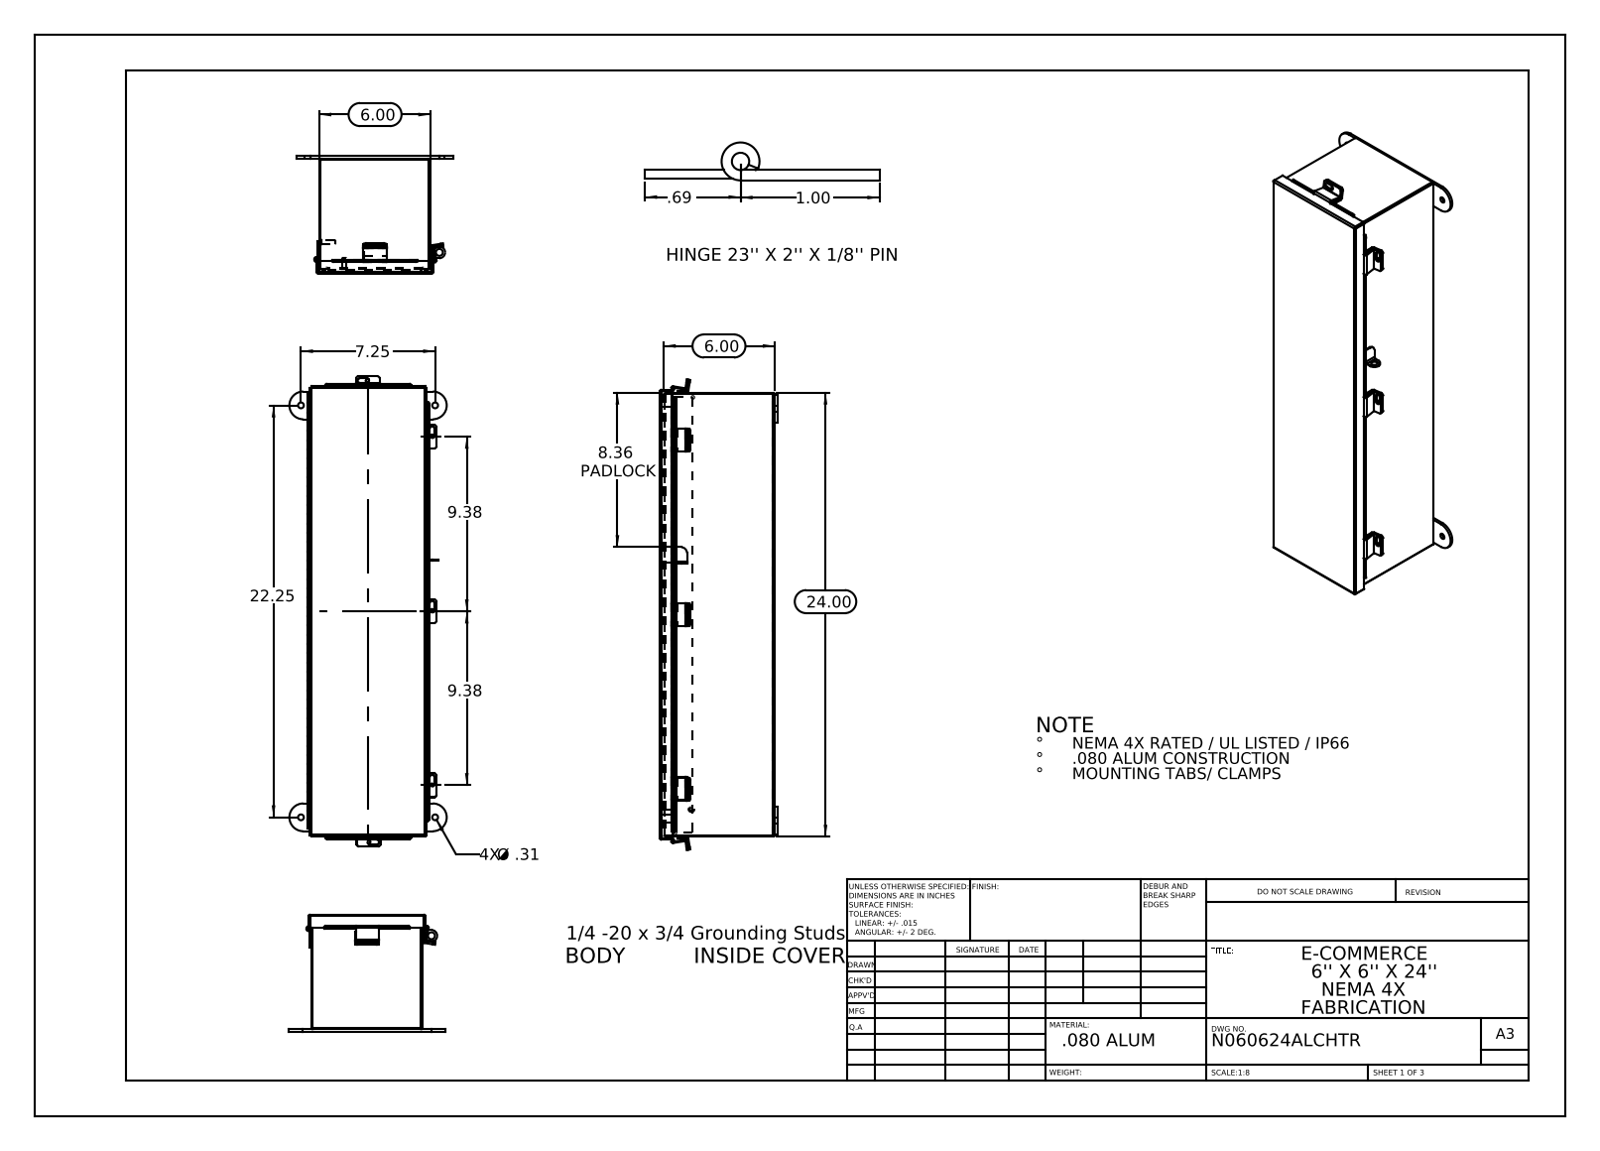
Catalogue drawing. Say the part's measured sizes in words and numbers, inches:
The part is named "N060624SSCHTR JIC Cover Clamp; N060624SSCHTR; N060624SSCHTR Mounting Bracket; N060624SSCHTR JIC Bottom (+8 more)". Its 3-D file was written by "SolidWorks 2013 (CONFIG_CONTROL_DESIGN)". It is 21 solids with 898 faces: 553 planar, 325 cylindrical and 20 other. Overall it measures 25.407 by 8.5 by 6.337 inches. Its volume is 60.62 cubic inches and its surface area 1 623 square inches. Round holes: 5 of diameter 0.25, 4 of diameter 0.313, 1 of diameter 0.125, 1 of diameter 0.125, 1 of diameter 0.375. Round bosses or shafts: 2 of diameter 0.315, 2 of diameter 0.236, 1 of diameter 0.273, 1 of diameter 0.25. Partial cylindrical surfaces (rounded edges, fillets, slot ends): 17 of radius 0.125, 12 of radius 0.009, 10 of radius 0.013, 10 of radius 0.088, 10 of radius 0.133, 6 of radius 0.083, 6 of radius 0.1, 4 of radius 0.75. The main face-to-face distances are 0.075, 5.925, 6.128, 6, 5.85, 6.203, 6.053, 23.925, 0.149, 6.074. The hole center spacings are 7.25, 9.425, 22.25, 23.402, 6.637, 18.85.
